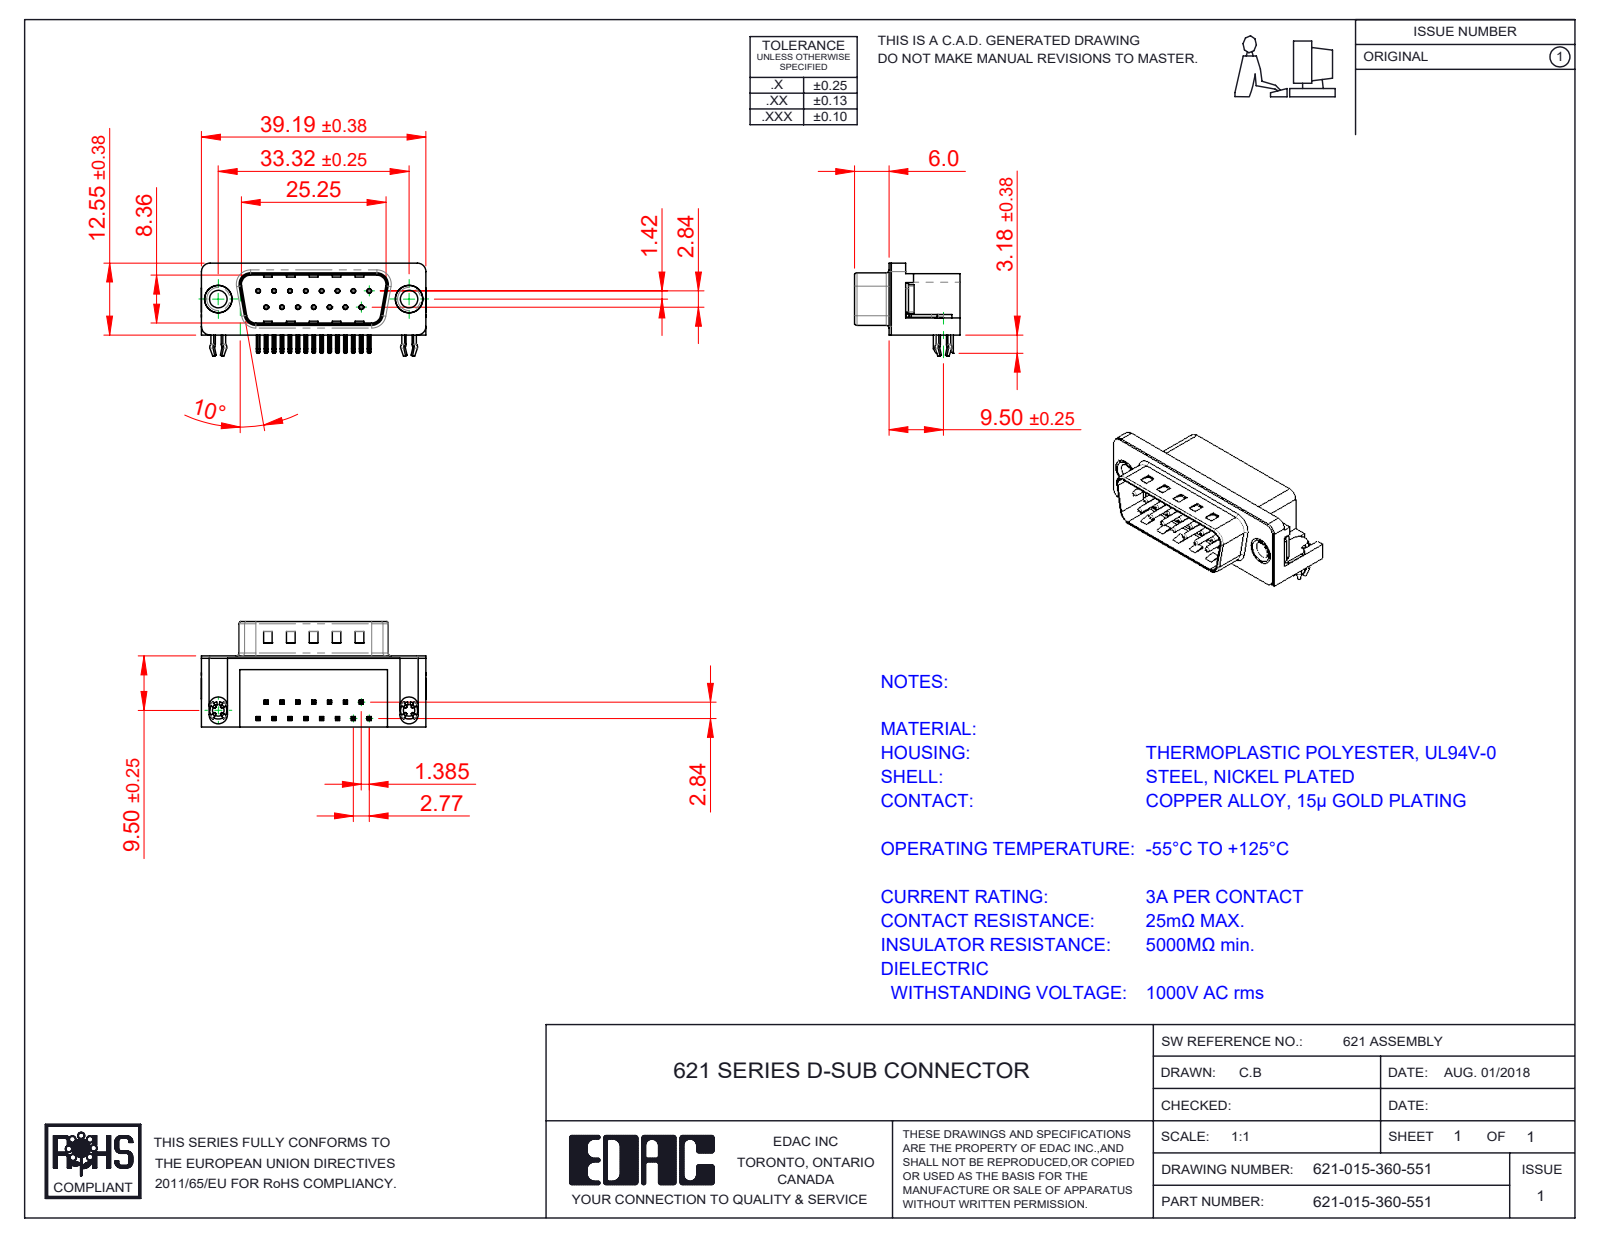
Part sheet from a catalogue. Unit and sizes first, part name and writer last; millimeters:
Units: millimetres
Overall size (bounding box): 39.22 × 18.4 × 15.73
Round holes (diameter × count): ⌀0.35 ×15, ⌀0.8 ×15, ⌀2.26 ×2, ⌀3.05 ×2, ⌀4 ×2, ⌀4.8 ×2, ⌀5 ×2
Round bosses / shafts (diameter × count): ⌀0.75 ×15, ⌀4.9 ×2, ⌀4.75 ×2, ⌀3.85 ×2, ⌀3.26 ×2
Partial cylindrical surfaces — rounded edges, fillets, slot ends (radius × count): R0.25 ×68, R0.12 ×30, R1 ×16, R0.5 ×9, R1.6 ×8, R1.5 ×6, R0.9 ×4, R2 ×4
Main face-to-face distances: 0.4, 12, 10.35, 2.1, 12.4, 10.46, 1.7, 10.86, 8.76, 2.9
Hole centre spacings: 3.16, 2.77, 5.54, 8.31, 11.08, 5.03, 5.04, 7.48
Volume: 4 414 mm³ · Surface area: 5 706 mm²
Bodies: 21 solids, 1467 faces (893 planar, 439 cylindrical, 135 other)
Part name (STEP PRODUCT): 621 4-40 Threaded Board Mount; 621 Thru Hole Rivet; 621 Shell_15 Socket; 621 Contact Bottom (+3 more)
STEP written by: SolidWorks 2016 (CONFIG_CONTROL_DESIGN)
